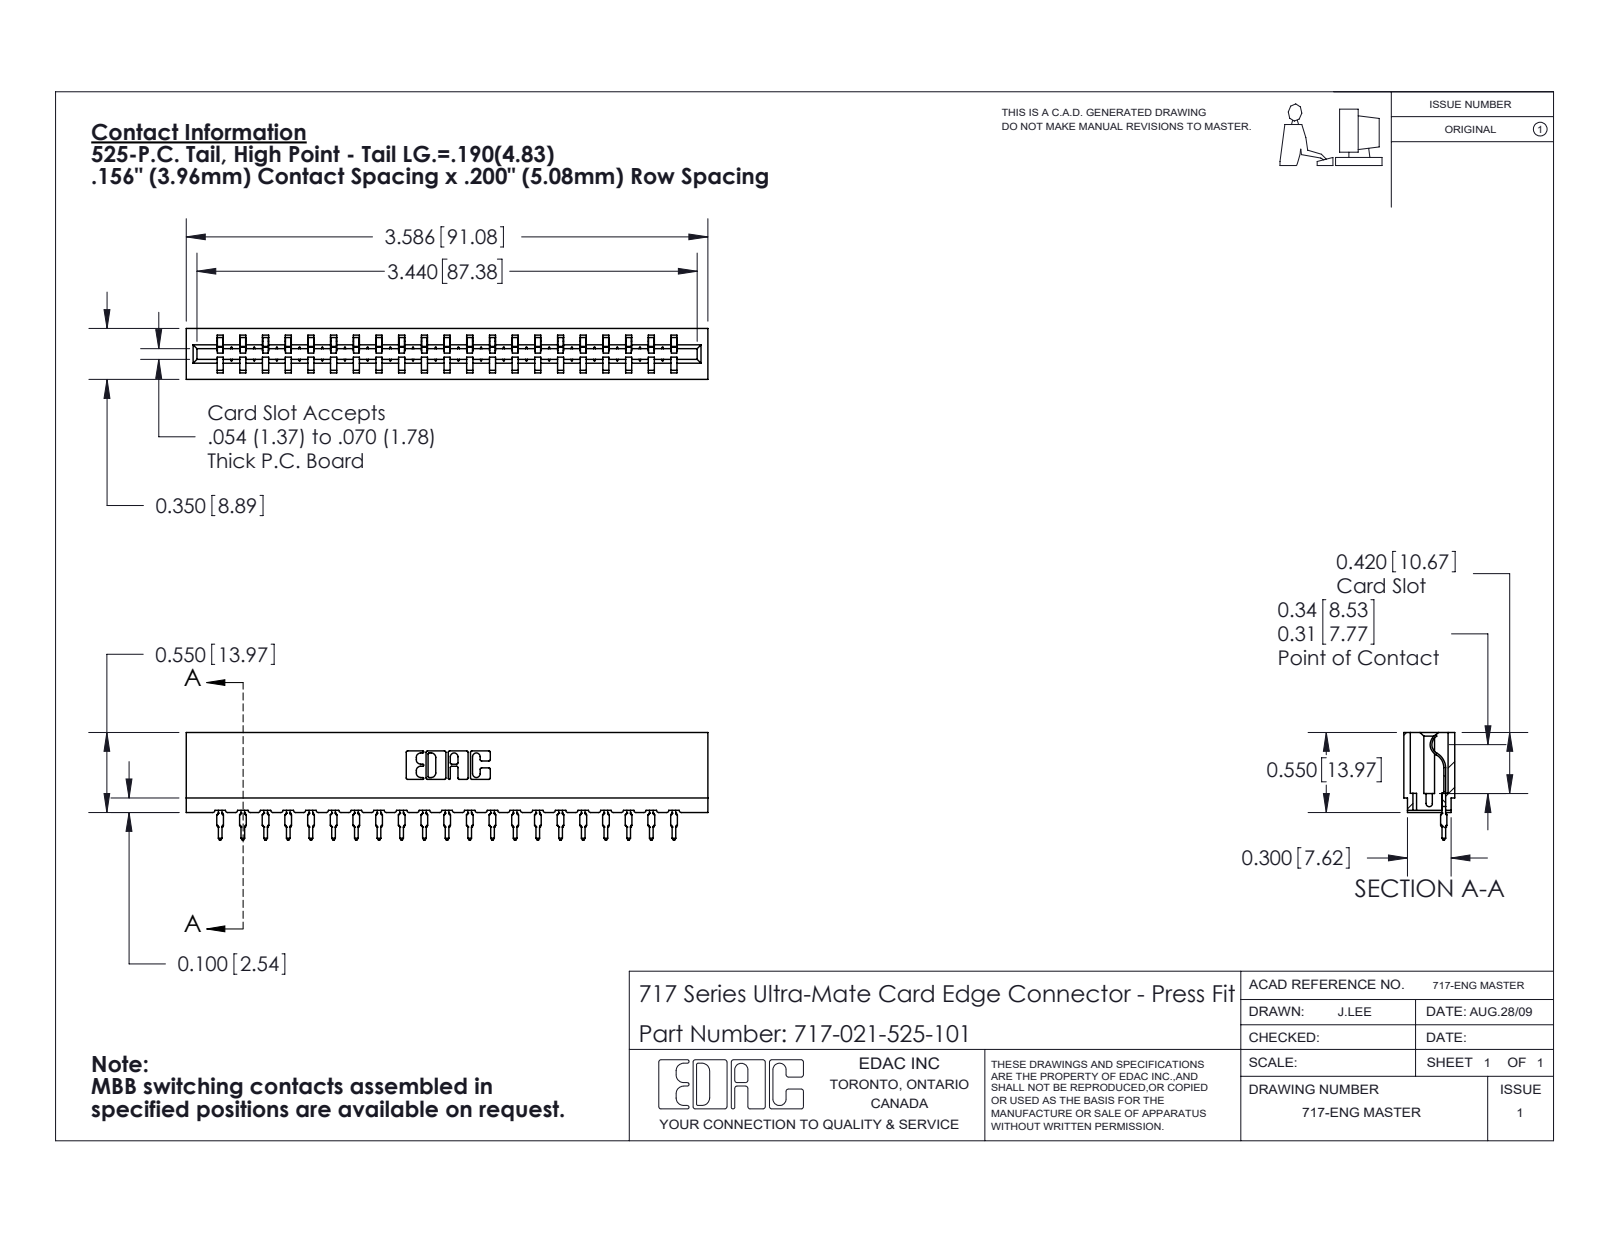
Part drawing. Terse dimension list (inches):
name: 717 Part_Insulator Option - 06; 745-292-001_525; 717-021-525-101
written by: SolidWorks 2020 (CONFIG_CONTROL_DESIGN)
unit: in
bodies: 22 solids, 2467 faces (1482 planar, 439 cylindrical, 546 other)
size: 3.586 × 0.739 × 0.35
volume: 0.474 in³; area: 16.46 in²
rounds: 42× R0.015, 42× R0.021, 22× R0.01, 6× R0.007, 6× R0.031, 4× R0.005, 4× R0.011, 3× R0.026
face distances: 0.212, 0.138, 0.35, 0.156, 0.624, 0.074, 0.468, 0.025, 0.045, 0.305
